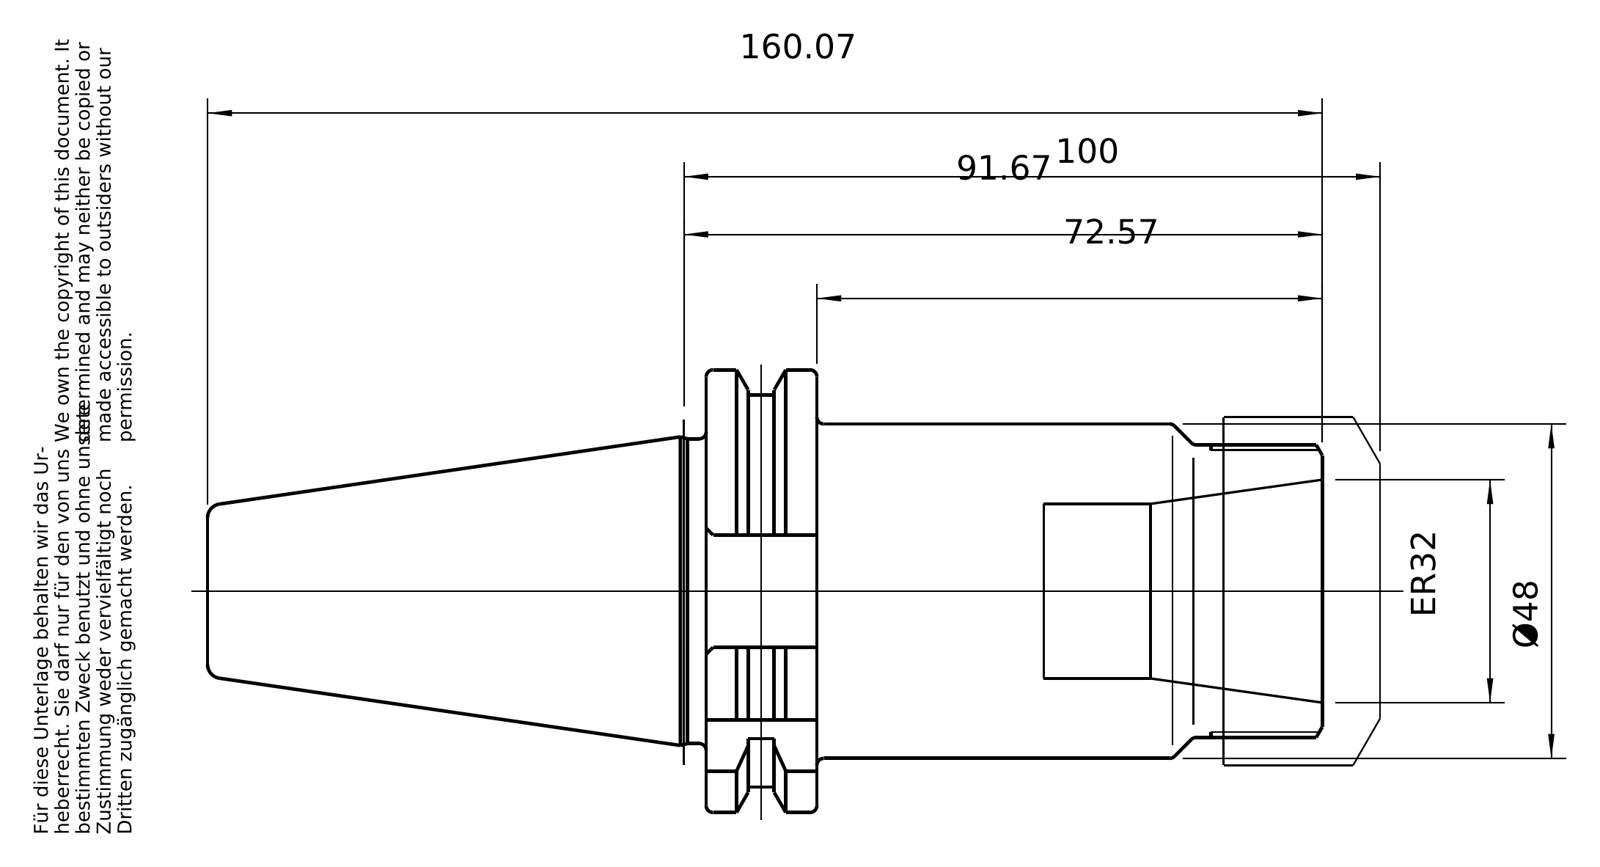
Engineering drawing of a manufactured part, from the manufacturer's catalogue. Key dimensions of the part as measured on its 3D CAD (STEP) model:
Part name (STEP PRODUCT): 40-321-32-3; 83-914-32; 40-321-32-3_ASM
STEP written by: PRO/ENGINEER BY PARAMETRIC TECHNOLOGY CORPORATION, 2010430 (CONFIG_CONTROL_DESIGN)
Units: millimetres
Bodies: 2 solids, 168 faces (32 planar, 52 cylindrical, 84 other)
Overall size (bounding box): 168.25 × 63.52 × 61.42
Volume: 223 301 mm³ · Surface area: 42 309 mm²
Round holes (diameter × count): ⌀2.5 ×1, ⌀13.84 ×1, ⌀17.01 ×1, ⌀17.5 ×1, ⌀25.07 ×1, ⌀27.3 ×1, ⌀35.9 ×1, ⌀38 ×1, ⌀42.7 ×1
Round bosses / shafts (diameter × count): ⌀50 ×1, ⌀48 ×1, ⌀43.75 ×1, ⌀42 ×1, ⌀16.01 ×1
Partial cylindrical surfaces — rounded edges, fillets, slot ends (radius × count): R3 ×8, R5 ×2, R16 ×2, R1.35 ×1, R7.89 ×1, R16.43 ×1, R28 ×1, R31.76 ×1
Main face-to-face distances: 15.85, 88.47, 72.62, 96.8, 80.95, 8.33, 48.47, 32.62, 40, 48.33
Hole centre spacings: 23
